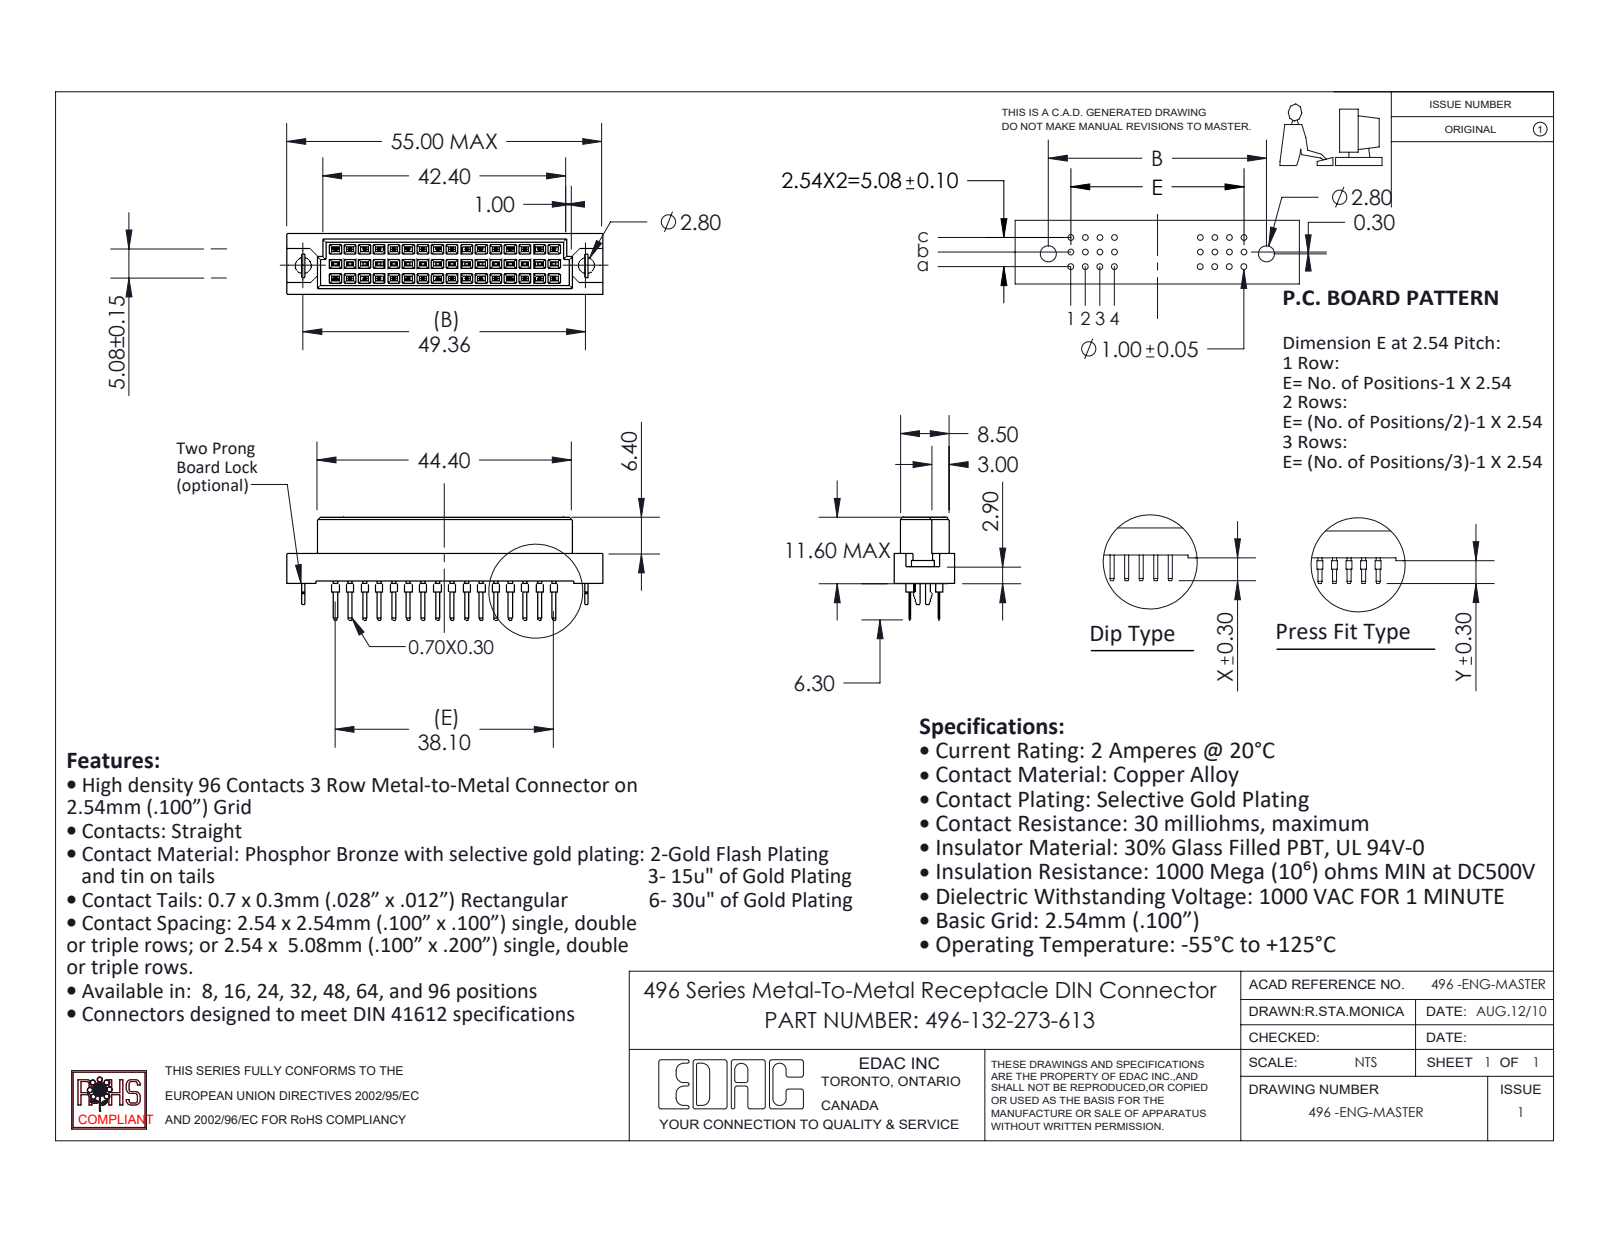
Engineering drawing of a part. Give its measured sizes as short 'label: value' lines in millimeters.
name: 496 Bore-lock; 496-290_73; 496-132-273-613; 496 Part_48
written by: SolidWorks 2020 (CONFIG_CONTROL_DESIGN)
unit: mm
bodies: 35 solids, 1278 faces (1208 planar, 70 cylindrical, 0 other)
size: 55 × 17.9 × 10.6
volume: 4 710 mm³; area: 5 101 mm²
holes: 2× ⌀2.8
bosses: 32× ⌀1
rounds: 1× R0.53
face distances: 2.54, 5.08, 1.05, 9.55, 0.81, 0.56, 0.55, 1.56, 1.86, 2.61
hole spacings: 49.36
